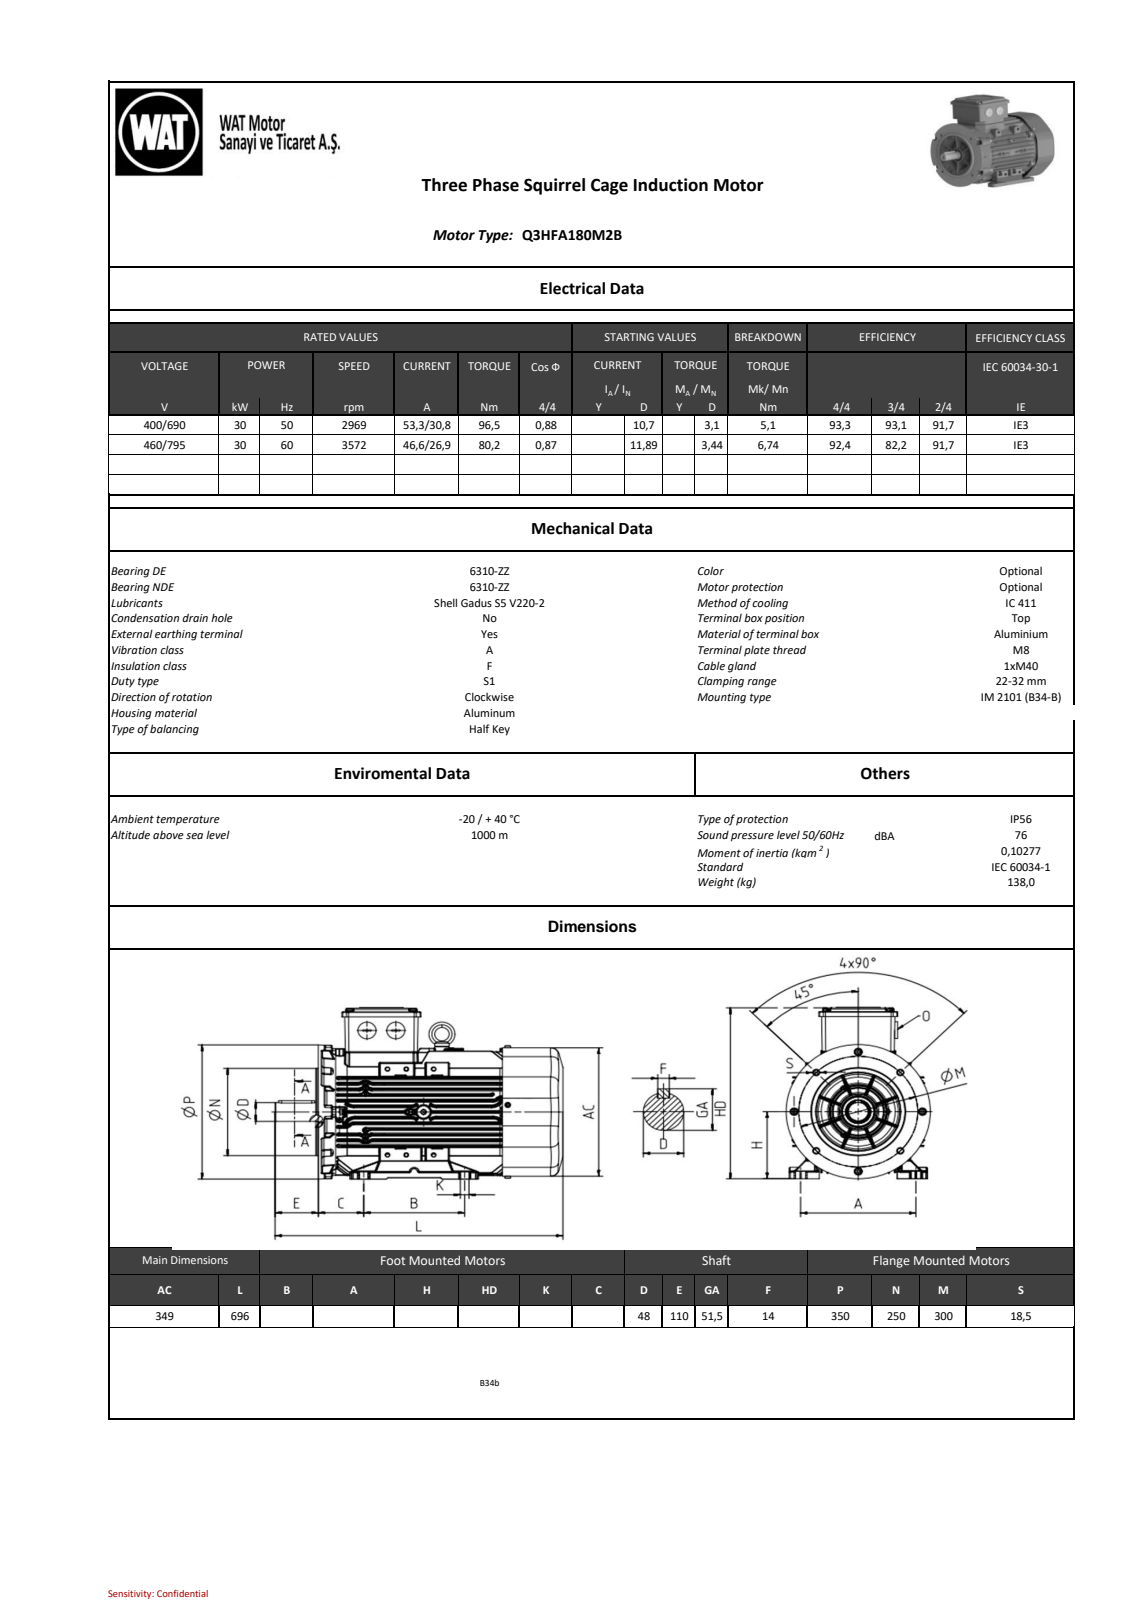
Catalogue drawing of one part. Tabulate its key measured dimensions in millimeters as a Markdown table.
| quantity | value |
| --- | --- |
| part name | 001_objects |
| STEP written by | SIEMENS PLM Software NX2206.8101 (AP203_CONFIGURATION_CONTROLLED_3D_DESIGN_OF_MECHANICAL_PARTS_AND_ASSEMBLIES_MIM_LF) |
| units | millimeters |
| bodies | 0 solids, 5233 faces (1744 planar, 1801 cylindrical, 1688 other) |
| overall size | 696 × 430.55 × 357.1 |
| round holes (diameter × count) | 19 × 4, 22 × 2, 25.05 × 2, 8 × 1, 80 × 1, 82 × 1, 240 × 1 |
| round bosses / shafts (diameter × count) | 12 × 4, 9.5 × 4, 8 × 4, 55 × 2, 51.2 × 2, 25 × 2, 303 × 1, 251 × 1 |
| partial cylindrical surfaces (radius × count) | 2 × 511, 1 × 471, 3 × 93, 0.5 × 33, 8 × 22, 1 × 18, 4 × 17, 5 × 14 |
| main face-to-face distances | 1.2, 16.21, 32.48, 16.27, 171.05, 173.83, 141.35, 157.62, 157.07, 140.86 |
| hole center spacings | 150.01, 212.14, 300.01, 52, 91, 137.03, 149.83, 149.84 |
